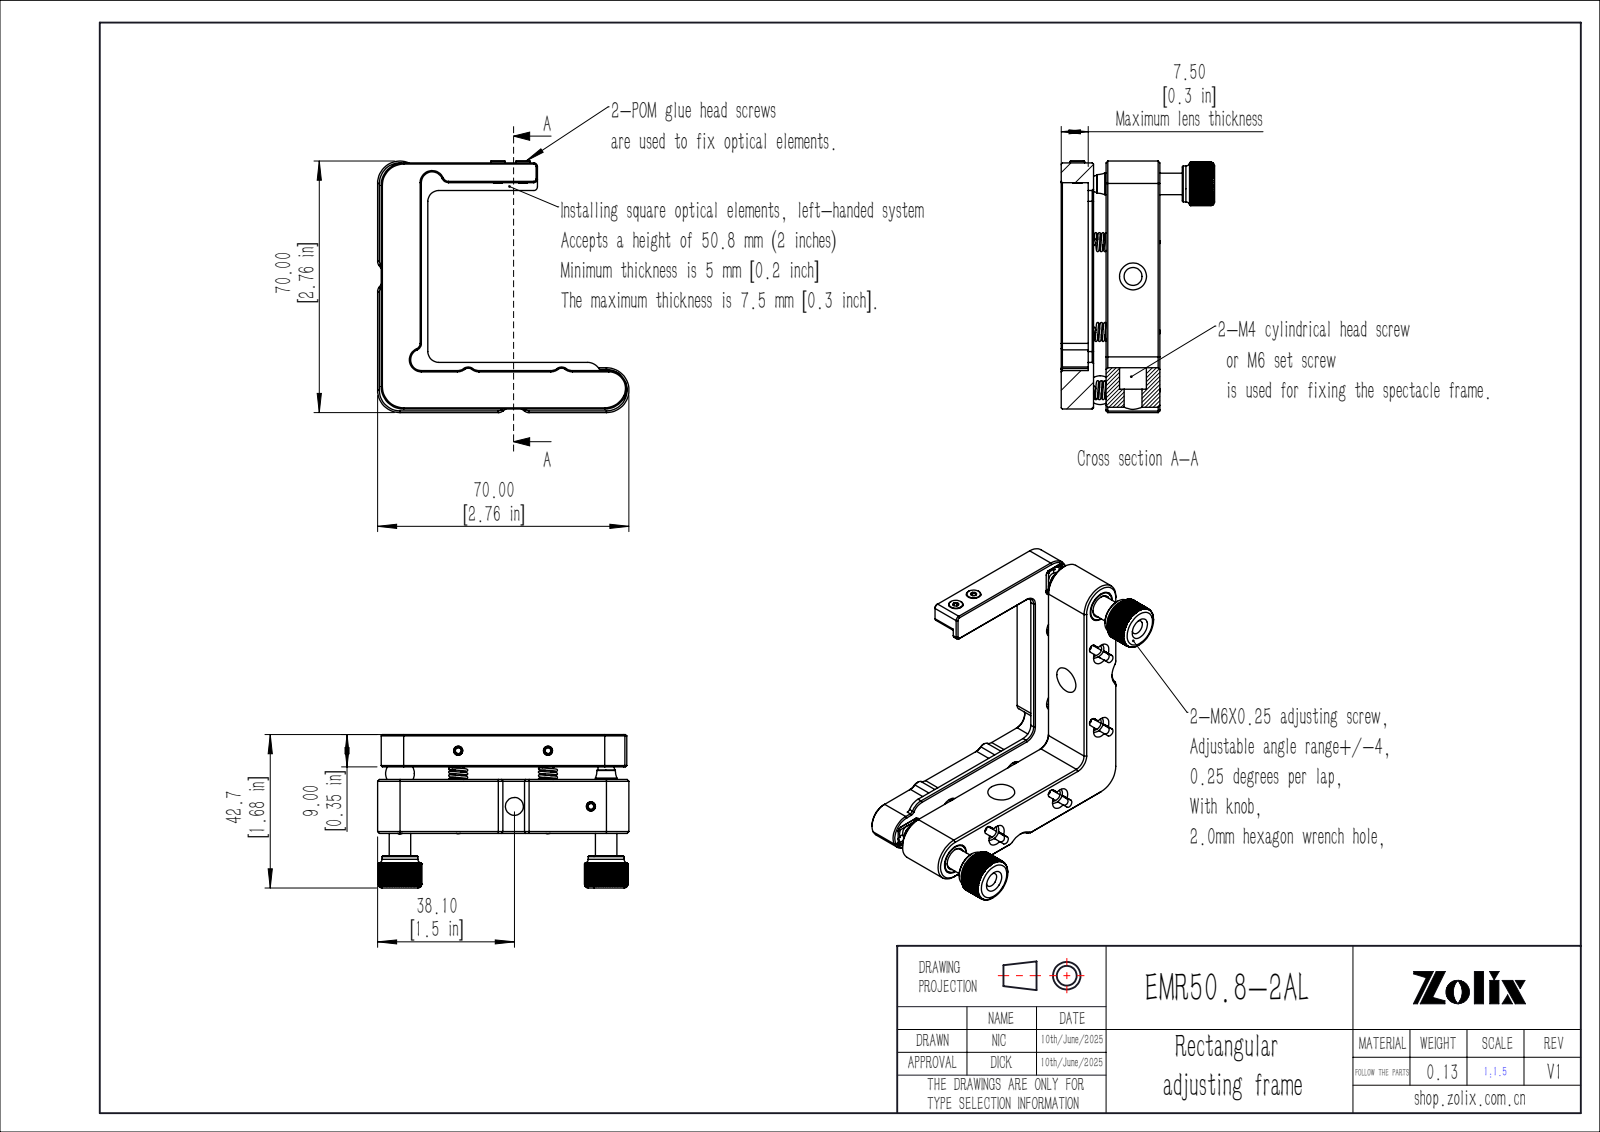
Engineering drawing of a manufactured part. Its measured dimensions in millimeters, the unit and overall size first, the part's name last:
Units: millimetres
Overall size (bounding box): 70 × 70 × 42.71
Round holes (diameter × count): ⌀6 ×4, ⌀3.3 ×2, ⌀5 ×2, ⌀7.5 ×2, ⌀8.6 ×2, ⌀9.5 ×2, ⌀9.8 ×2, ⌀10 ×2
Round bosses / shafts (diameter × count): ⌀4 ×4, ⌀2 ×4, ⌀1.5 ×4, ⌀6 ×2, ⌀2.4 ×2
Partial cylindrical surfaces — rounded edges, fillets, slot ends (radius × count): R3 ×9, R0.8 ×8, R1.1 ×8, R2 ×8, R6.25 ×6, R1 ×4, R2.5 ×2, R4.83 ×2
Main face-to-face distances: 12.5, 9, 18.5, 27.5, 15, 3.5, 1, 11.5, 1.5, 5
Hole centre spacings: 16.2, 25, 41.2, 44.27, 59.64, 70.66, 7, 15.68
Bodies: 0 solids, 1007 faces (496 planar, 278 cylindrical, 233 other)
Part name (STEP PRODUCT): EMR50.8-2AL
STEP written by: SolidWorks 2020 (CONFIG_CONTROL_DESIGN)
